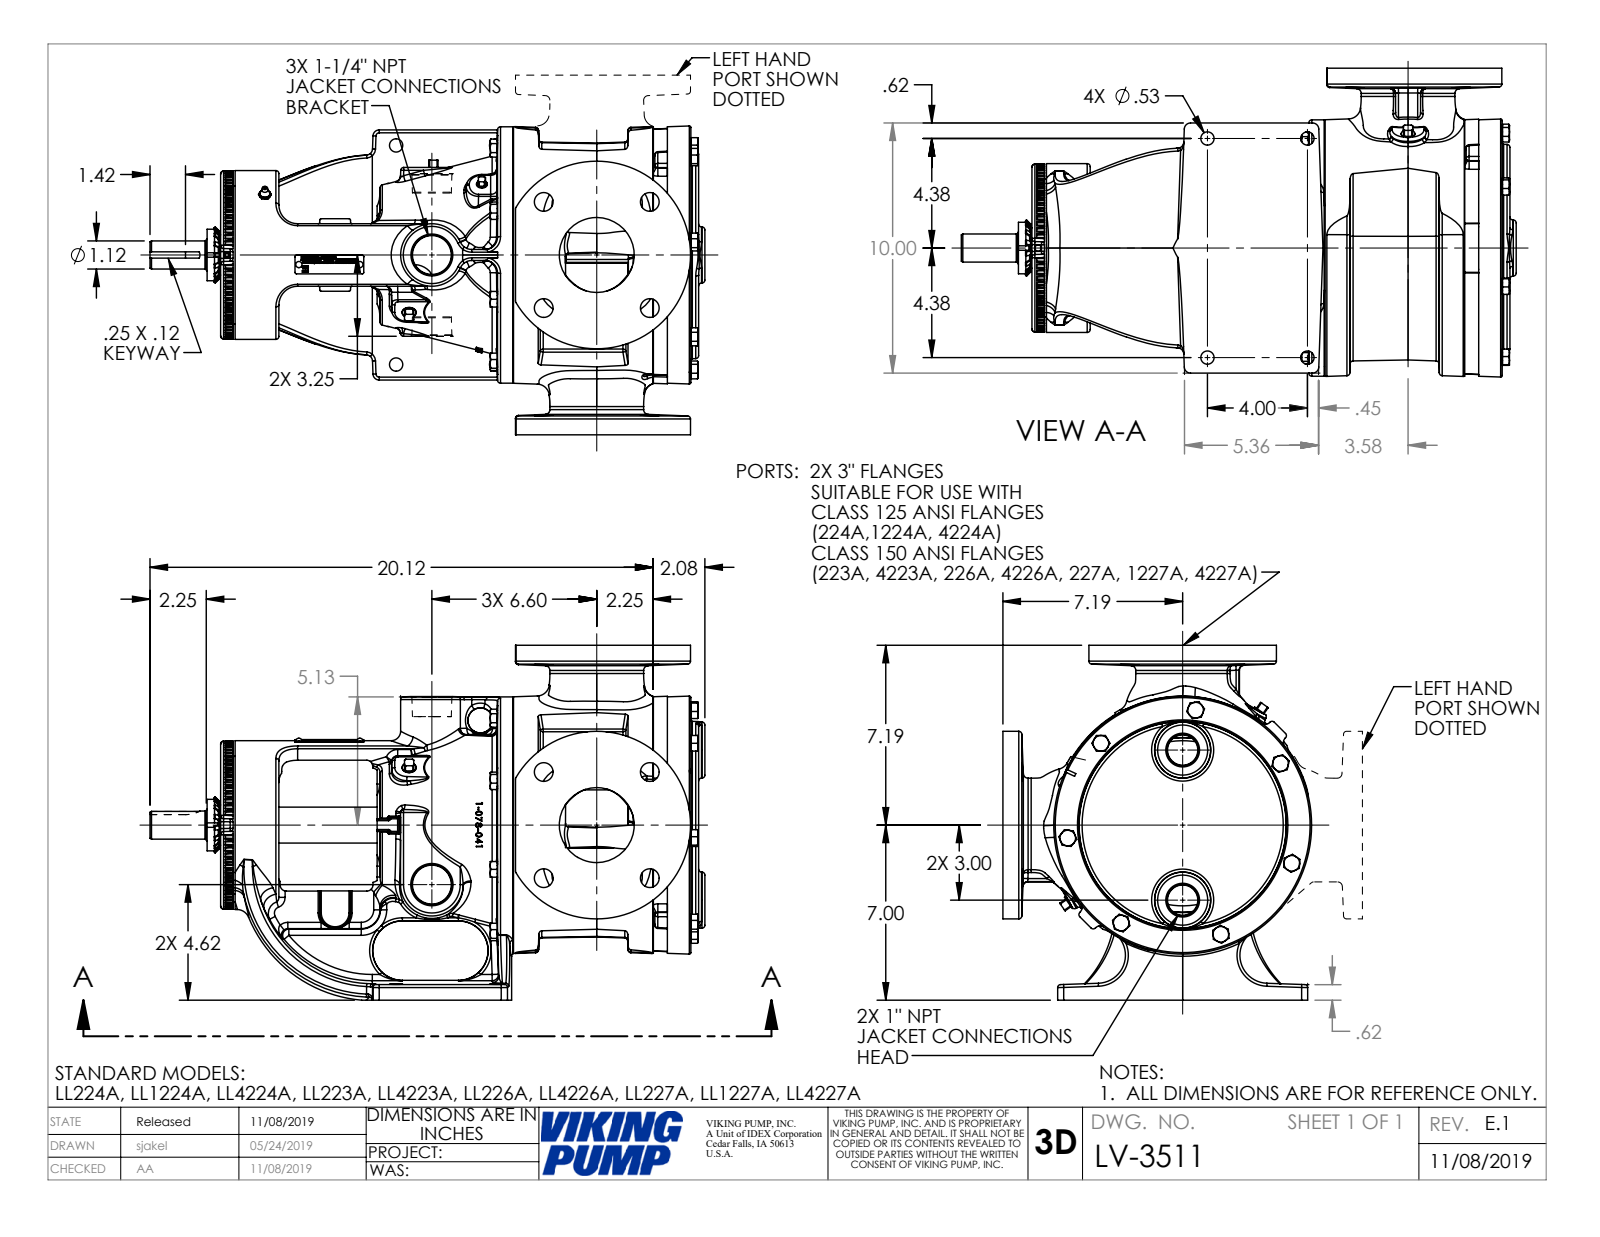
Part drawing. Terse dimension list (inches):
name: LV-3511
written by: SolidWorks 2024 (AUTOMOTIVE_DESIGN)
unit: in
bodies: 1 solid, 2954 faces (1012 planar, 400 cylindrical, 1542 other)
size: 22.195 × 14.19 × 12.489
volume: 1 083 in³; area: 1 316 in²
holes: 8× ⌀0.75, 6× ⌀0.197, 6× ⌀0.25, 4× ⌀0.531, 2× ⌀0.313, 2× ⌀1.094, 1× ⌀0.257, 1× ⌀1.38, 1× ⌀1.387, 1× ⌀1.71, 1× ⌀2.312, 1× ⌀2.69
bosses: 11× ⌀0.625, 4× ⌀0.625, 2× ⌀7.5, 2× ⌀3.75, 1× ⌀10.25, 1× ⌀6.75, 1× ⌀5.497, 1× ⌀5.247
rounds: 75× R0.12, 37× R0.06, 22× R0.25, 16× R0.12, 8× R0.03, 8× R0.75, 6× R0.547, 4× R0.237
face distances: 14.19, 0.31, 18.81, 19.12, 1, 1.75, 0.58, 18.23, 18.54, 3.93
hole spacings: 3, 1.03, 4.243, 2.385, 2.909, 3.799, 2.022, 6
